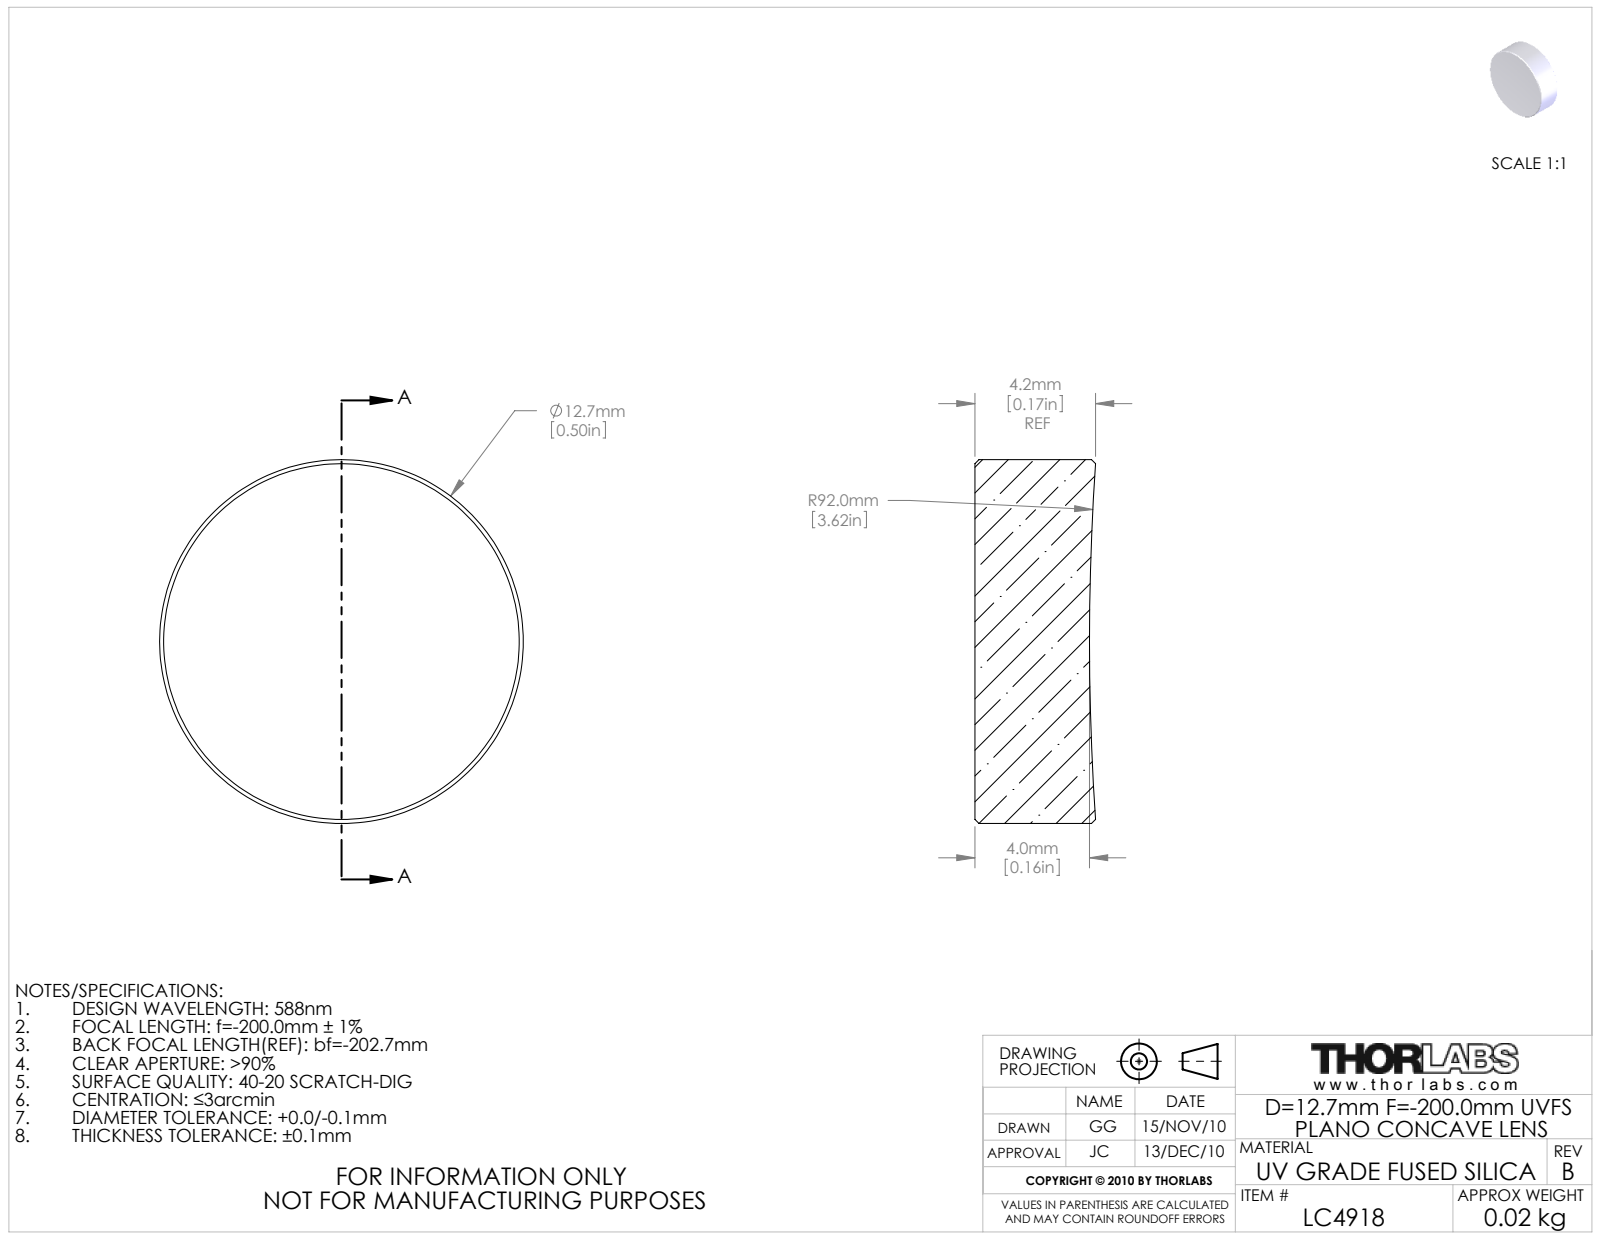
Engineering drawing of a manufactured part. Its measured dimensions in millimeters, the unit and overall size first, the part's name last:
Units: millimetres
Overall size (bounding box): 12.7 × 12.7 × 4.21
Round bosses / shafts (diameter × count): ⌀12.7 ×1
Volume: 520 mm³ · Surface area: 415 mm²
Bodies: 1 solid, 9 faces (1 planar, 2 cylindrical, 6 other)
Part name (STEP PRODUCT): 3500-E0W
STEP written by: SolidWorks 2009 (AUTOMOTIVE_DESIGN)
